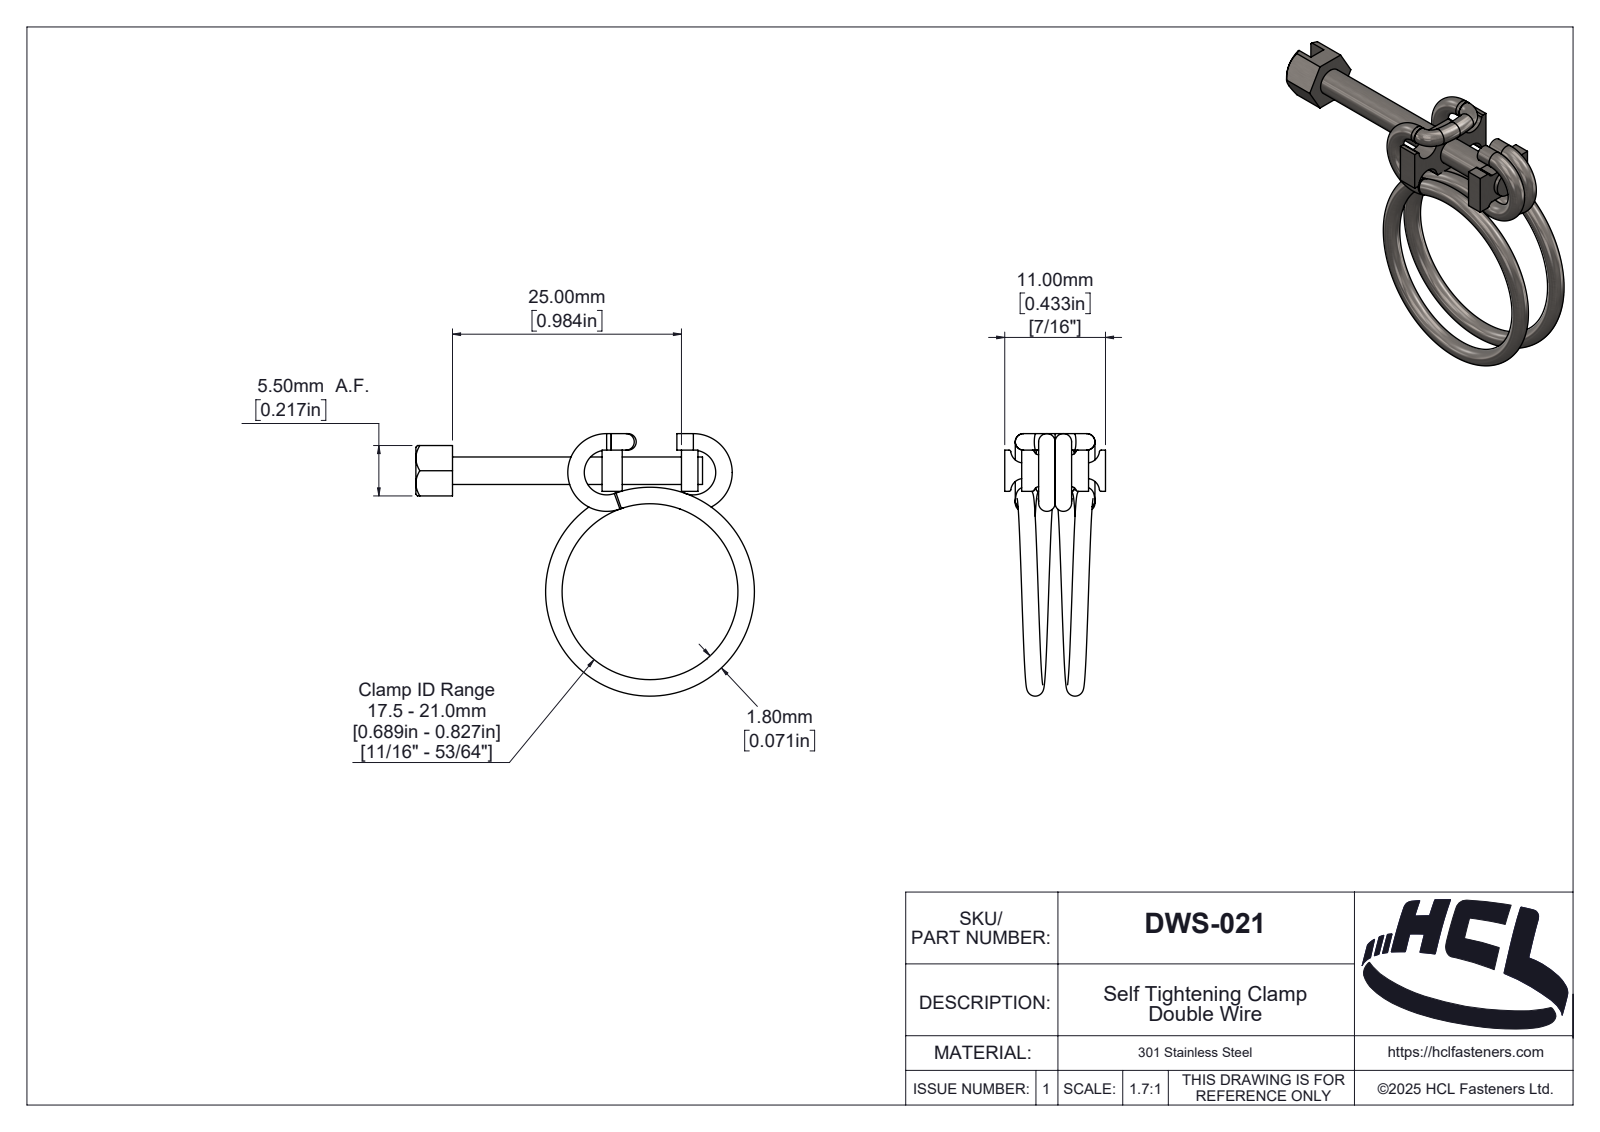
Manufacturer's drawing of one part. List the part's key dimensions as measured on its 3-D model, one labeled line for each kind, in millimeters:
Part name (STEP PRODUCT): DWS-021
STEP written by: SolidWorks 2025 (AUTOMOTIVE_DESIGN)
Units: millimetres
Bodies: 6 solids, 209 faces (51 planar, 74 cylindrical, 84 other)
Overall size (bounding box): 36.97 × 28.65 × 11
Volume: 906 mm³ · Surface area: 1 849 mm²
Round holes (diameter × count): ⌀3 ×1
Round bosses / shafts (diameter × count): ⌀1.8 ×4
Partial cylindrical surfaces — rounded edges, fillets, slot ends (radius × count): R0.2 ×12, R0.5 ×4, R1.4 ×4, R0.4 ×1, R0.51 ×1, R0.53 ×1, R0.64 ×1, R0.91 ×1
Main face-to-face distances: 4.5, 0.5, 2, 5.5, 2.2, 4, 1, 8.66, 6.46, 10.46
